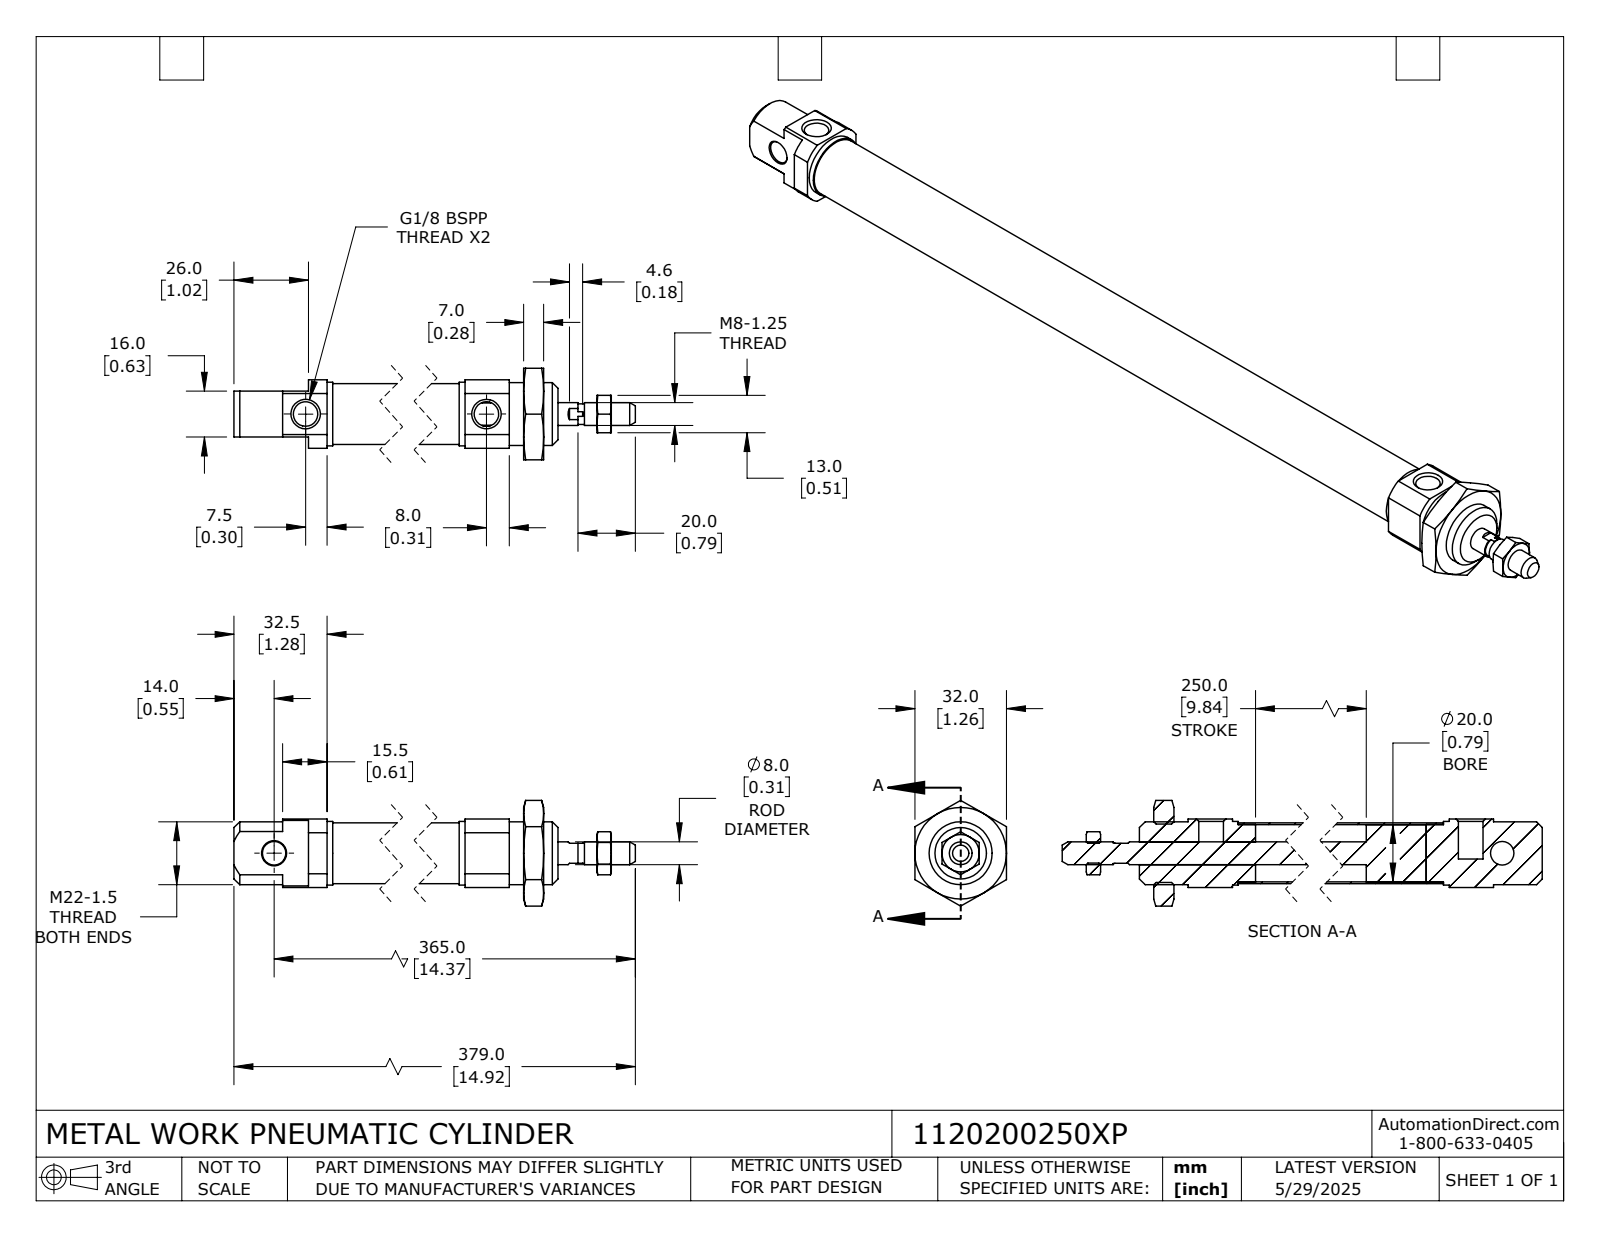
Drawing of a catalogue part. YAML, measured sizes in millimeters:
part_name: "1120200250XP; 1120200250XP_ROD; 1120200250XP_BODY"
step_written_by: "SolidWorks 2024 (CONFIG_CONTROL_DESIGN)"
units: millimeters
bodies: {solids: 6, faces: 147, planar: 56, cylindrical: 45, other: 46}
overall_size: [379, 36.95, 32]
volume: 66563
surface_area: 59059
round_holes:
  - {diameter: 8.57, count: 2}
  - {diameter: 6.92, count: 1}
  - {diameter: 8.2, count: 1}
  - {diameter: 20, count: 1}
  - {diameter: 20.38, count: 1}
round_bosses_or_shafts:
  - {diameter: 22.2, count: 1}
  - {diameter: 22, count: 1}
  - {diameter: 21.27, count: 1}
  - {diameter: 20.15, count: 1}
  - {diameter: 8, count: 1}
  - {diameter: 7.2, count: 1}
partial_cylinders:
  - {radius: 13.95, count: 1}
face_to_face_distances: [3.97, 19.97, 23.94, 8, 40.5, 311.5, 7, 5, 306.5, 299.5]
hole_center_spacings: [302]
